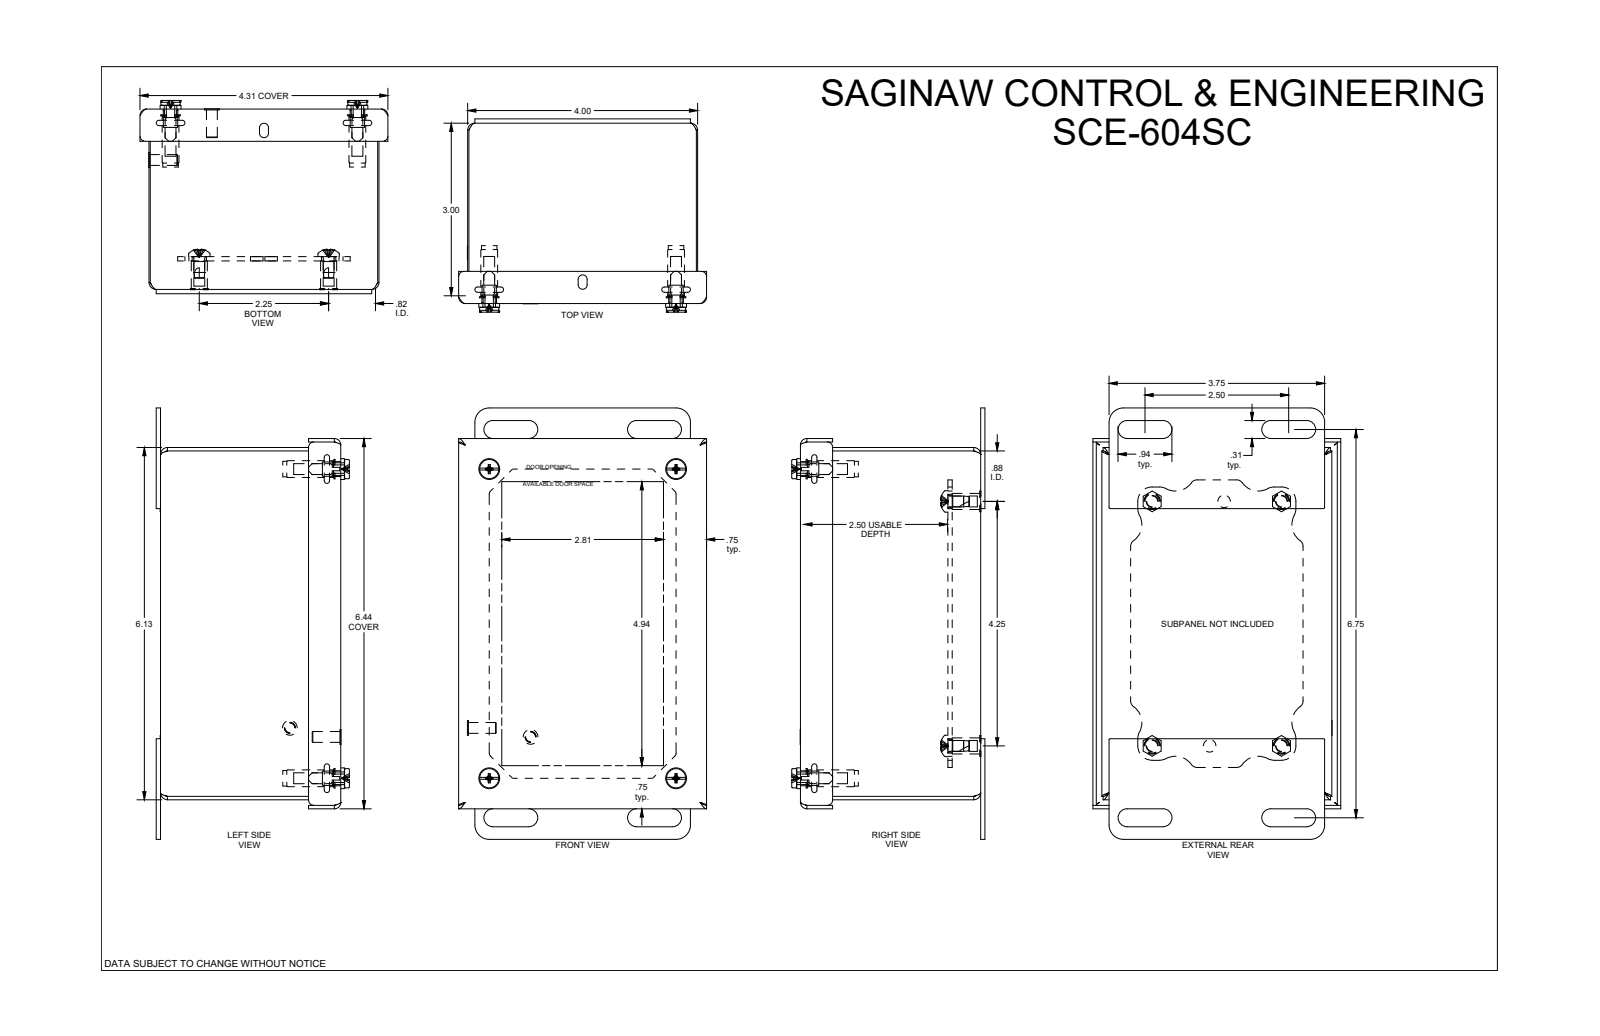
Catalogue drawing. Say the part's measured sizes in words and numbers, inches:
The part is named "SCE-604SC". Its 3-D file was written by "SolidWorks 2021 (AUTOMOTIVE_DESIGN)". It is 23 solids with 745 faces: 285 planar, 195 cylindrical and 265 other. Overall it measures 7.5 by 4.313 by 3.361 inches. Its volume is 10.32 cubic inches and its surface area 336 square inches. Round holes: 8 of diameter 0.25, 4 of diameter 0.19, 4 of diameter 0.22, 4 of diameter 0.266, 4 of diameter 0.281, 4 of diameter 0.317, 2 of diameter 0.218, 1 of diameter 0.187, 1 of diameter 0.193. Round bosses or shafts: 9 of diameter 0.188, 4 of diameter 0.437, 4 of diameter 0.373, 4 of diameter 0.362, 4 of diameter 0.34, 4 of diameter 0.334, 4 of diameter 0.292, 4 of diameter 0.27. Partial cylindrical surfaces (rounded edges, fillets, slot ends): 16 of radius 0.125, 16 of radius 0.25, 12 of radius 0.06, 8 of radius 0.005, 8 of radius 0.05, 8 of radius 0.063, 8 of radius 0.156, 8 of radius 0.255. The main face-to-face distances are 0.06, 3.075, 3.94, 3.135, 3.015, 6.065, 2.505, 0.075, 4, 3.88. The hole center spacings are 2.807, 0.752, 5.543, 6.281, 4.839, 0.753, 2.25, 3.25.
